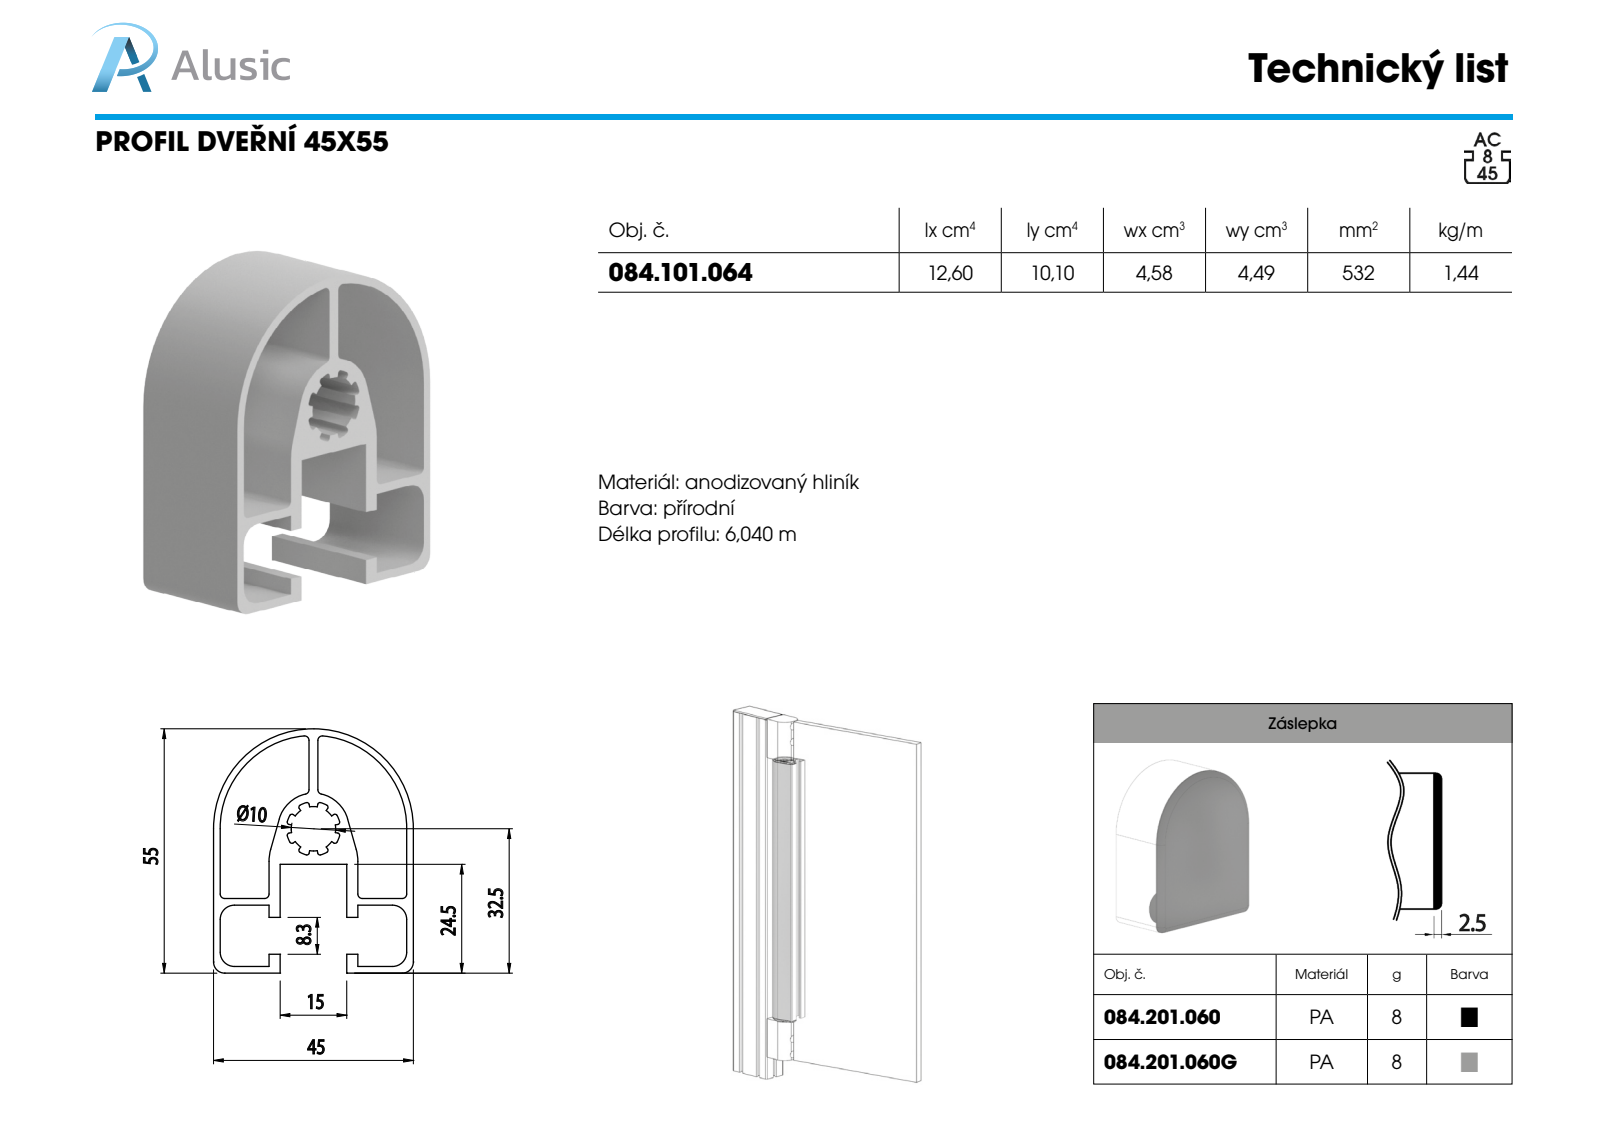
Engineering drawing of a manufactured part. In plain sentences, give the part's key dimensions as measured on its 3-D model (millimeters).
The part is named "084.101.064". Its 3-D file was written by "SolidWorks 2018 (AUTOMOTIVE_DESIGN)". It is 1 solid with 113 faces: 51 planar, 62 cylindrical and 0 other. Overall it measures 100 by 55 by 45 millimeters. Its volume is 53 259 cubic millimeters and its surface area 55 297 square millimeters. Partial cylindrical surfaces (rounded edges, fillets, slot ends): 16 of radius 0.5, 8 of radius 1, 4 of radius 3.2, 2 of radius 2.5, 1 of radius 5, 1 of radius 6.1, 1 of radius 8, 1 of radius 10. The main face-to-face distances are 1.5, 11, 43.5, 20, 15.3, 45, 12.5, 32.5, 31, 21.5.
